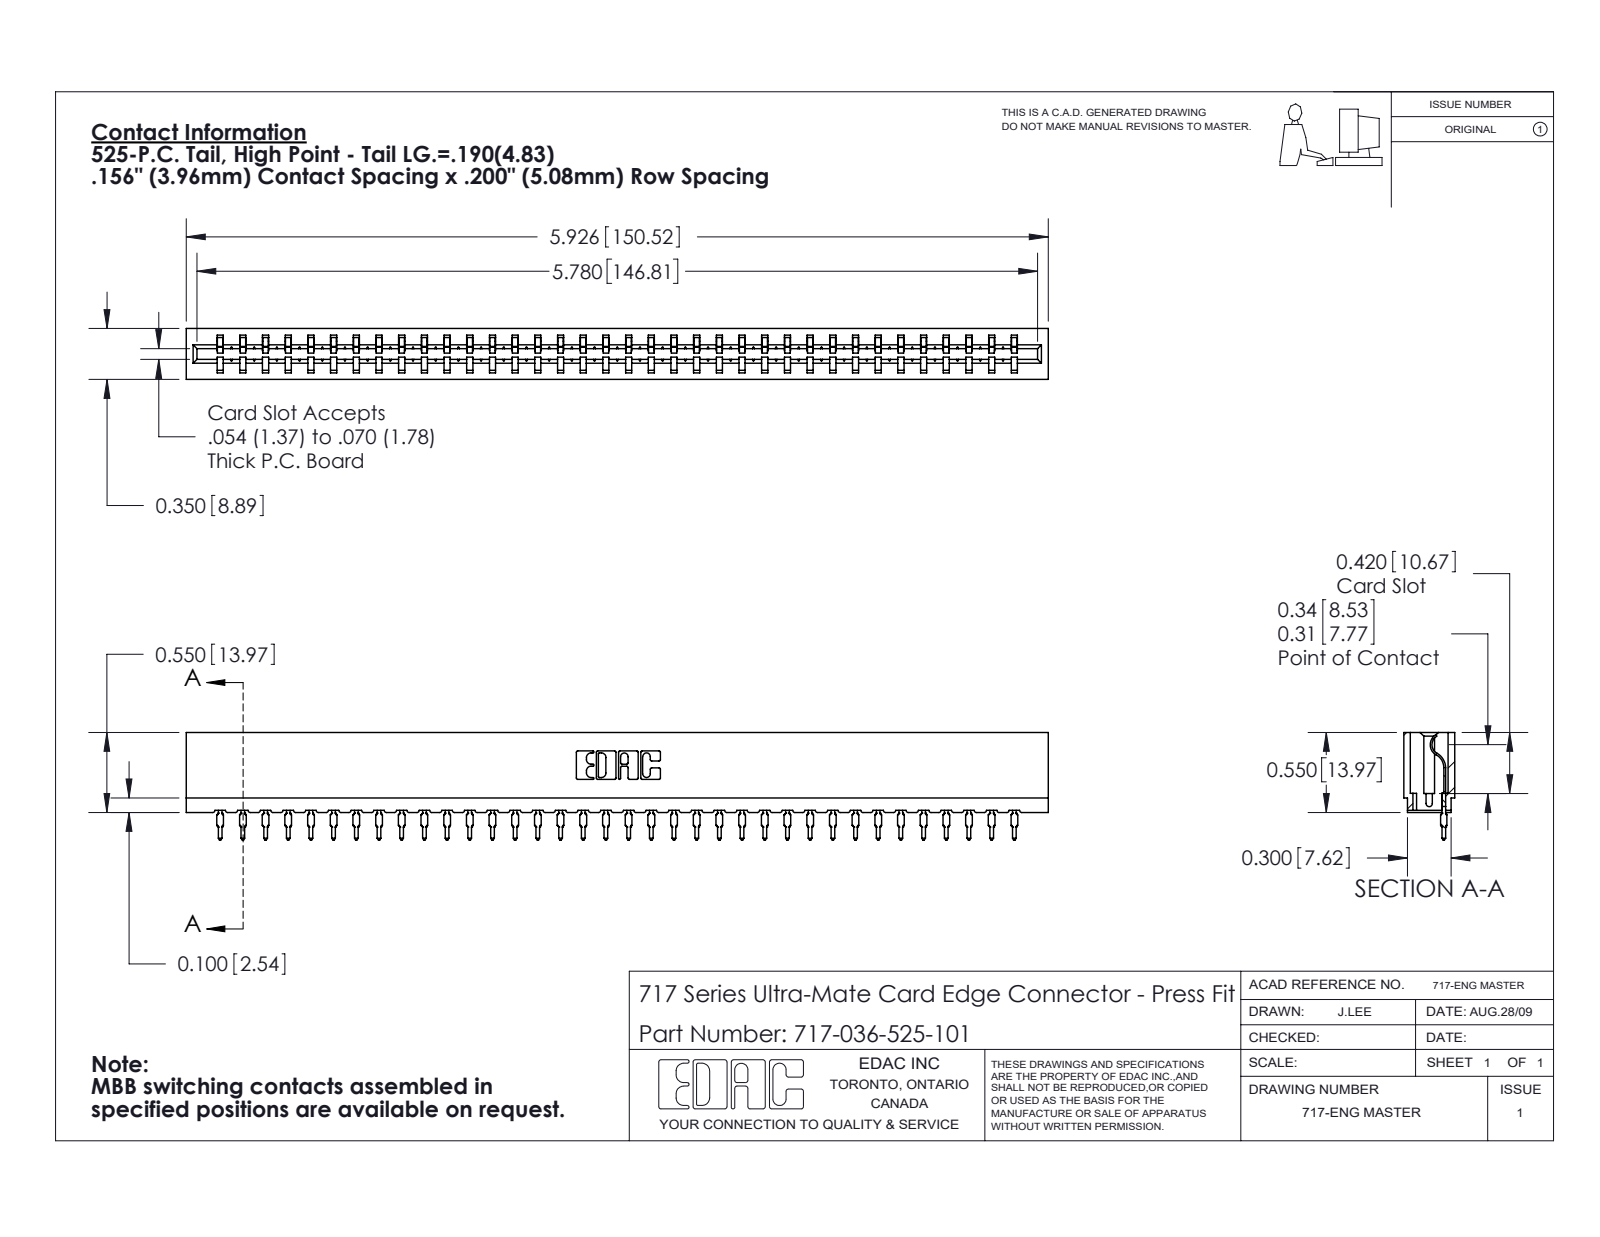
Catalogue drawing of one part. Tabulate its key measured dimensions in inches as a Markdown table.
| quantity | value |
| --- | --- |
| part name | 745-292-001_525; 717-036-525-101; 717 Part_Insulator Option - 06 |
| STEP written by | SolidWorks 2020 (CONFIG_CONTROL_DESIGN) |
| units | inches |
| bodies | 37 solids, 4162 faces (2502 planar, 724 cylindrical, 936 other) |
| overall size | 5.926 × 0.739 × 0.35 |
| volume | 0.775 in³ |
| surface area | 27.39 in² |
| partial cylindrical surfaces (radius × count) | 0.015 × 72, 0.021 × 72, 0.01 × 22, 0.007 × 6, 0.031 × 6, 0.005 × 4, 0.011 × 4, 0.026 × 3 |
| main face-to-face distances | 0.212, 0.138, 0.35, 0.074, 0.045, 0.305, 0.093, 0.167, 0.025, 0.063 |
